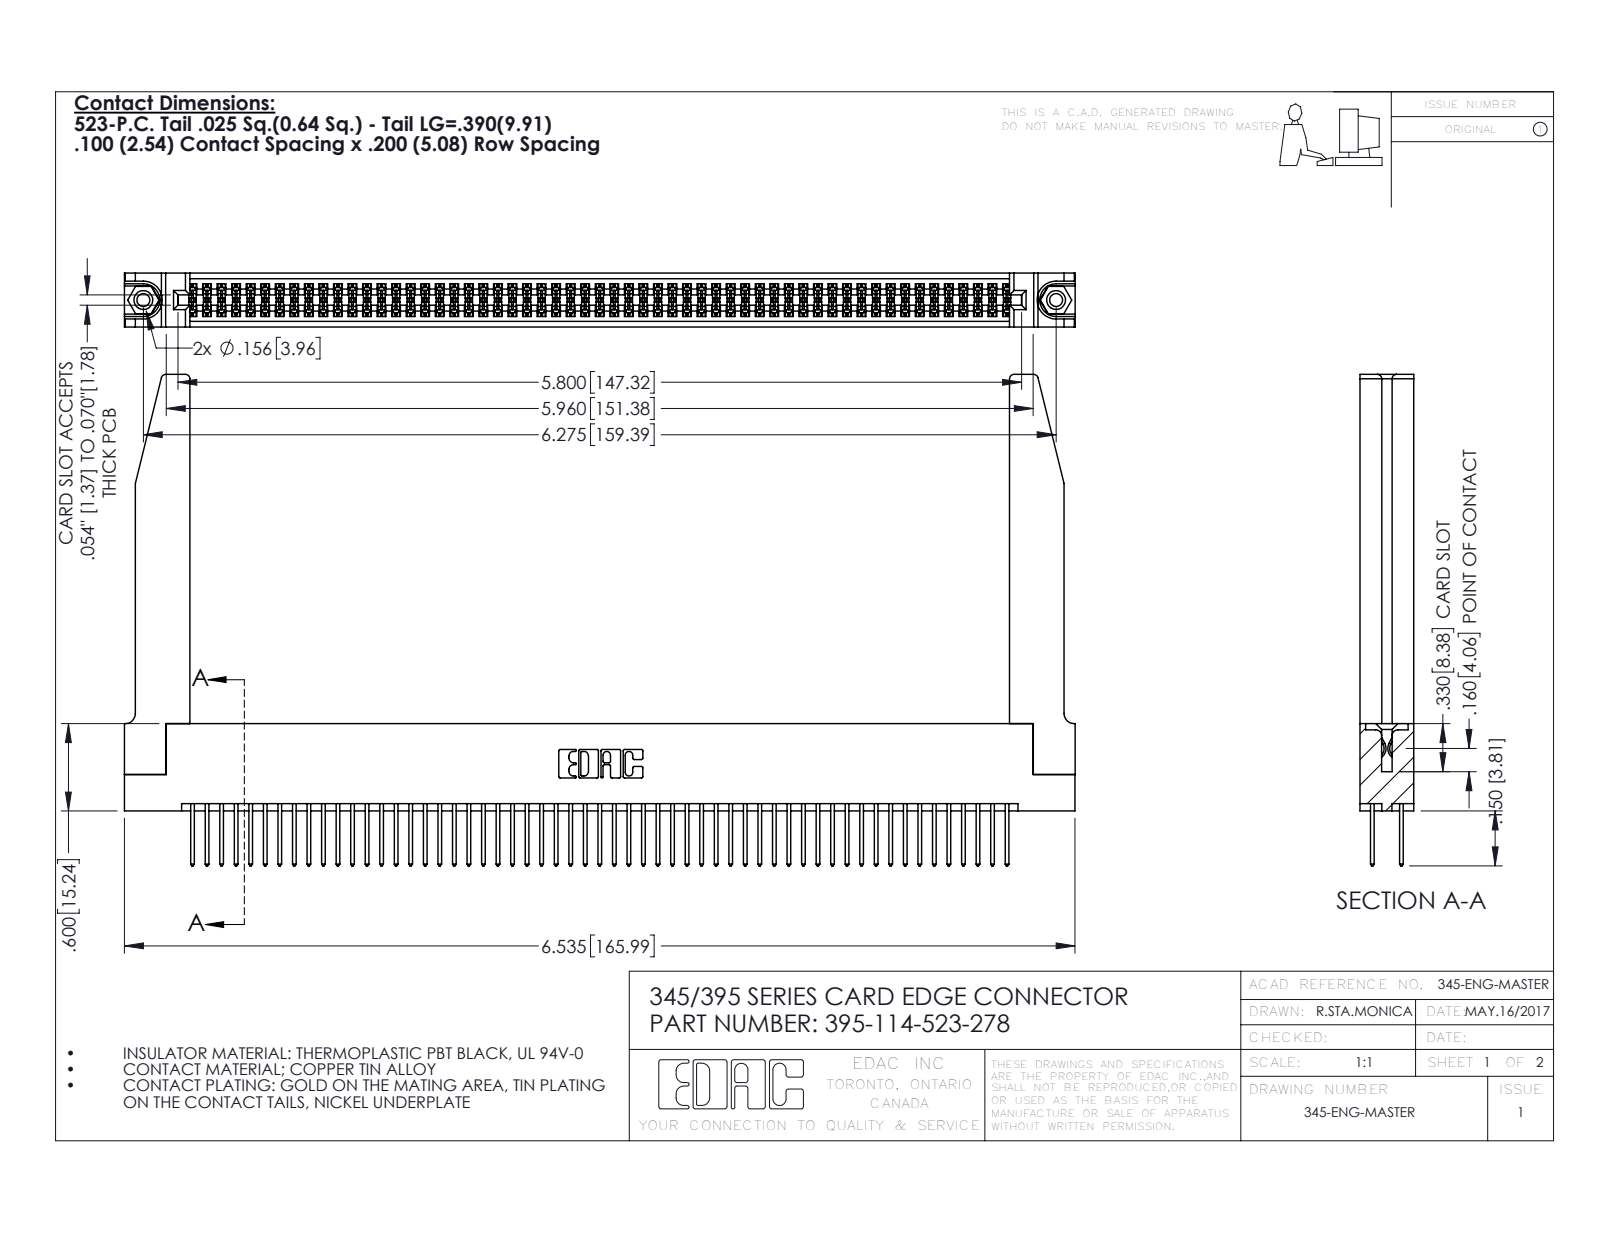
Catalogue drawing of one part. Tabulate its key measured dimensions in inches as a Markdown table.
| quantity | value |
| --- | --- |
| part name | 345-292-001_345-293-123; 345-220-078_345-220-078; 345 Part_Flush Mounting Lugs - 0.156 Dia-TH; 395-114-523-278 (+1 more) |
| STEP written by | SolidWorks 2016 (CONFIG_CONTROL_DESIGN) |
| units | inches |
| bodies | 119 solids, 6060 faces (3984 planar, 2024 cylindrical, 52 other) |
| overall size | 6.536 × 3.377 × 0.37 |
| volume | 1.481 in³ |
| surface area | 50.48 in² |
| round holes (diameter × count) | 0.089 × 2, 0.125 × 2, 0.156 × 2, 0.064 × 1 |
| round bosses / shafts (diameter × count) | 0.155 × 2 |
| partial cylindrical surfaces (radius × count) | 0.006 × 171, 0.01 × 114, 0.01 × 22, 0.03 × 8, 0.007 × 6, 0.031 × 6, 0.026 × 3, 0.014 × 2 |
| main face-to-face distances | 0.072, 0.298, 0.37, 0.2, 0.098, 0.272, 0.025, 0.225, 0.175, 0.148 |
| hole center spacings | 0.27, 6.039, 6.275 |
